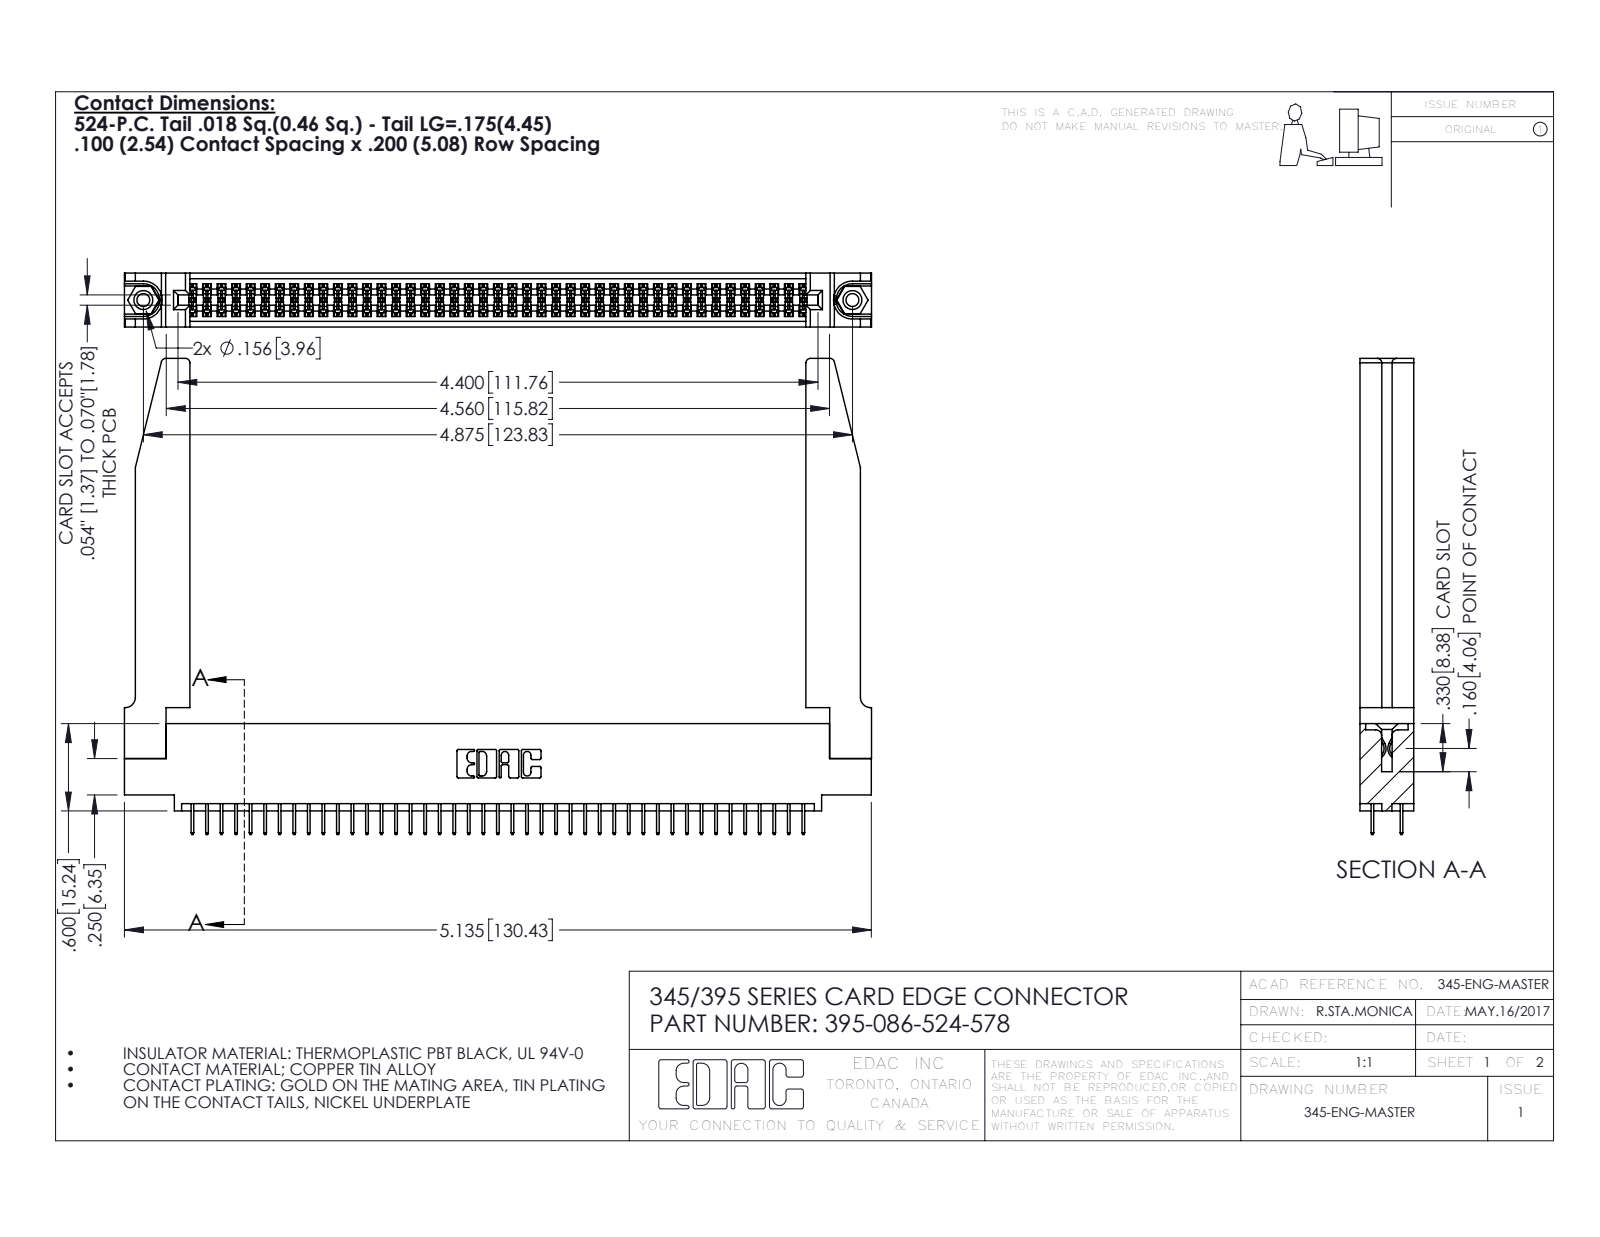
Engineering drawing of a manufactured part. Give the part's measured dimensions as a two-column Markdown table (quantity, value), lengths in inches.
| quantity | value |
| --- | --- |
| part name | 345-292-001_345-293-124; 345-250-001_345-250-001-102; 395-086-524-578; 345-220-078_345-220-078 (+1 more) |
| STEP written by | SolidWorks 2016 (CONFIG_CONTROL_DESIGN) |
| units | inches |
| bodies | 91 solids, 5008 faces (3580 planar, 1376 cylindrical, 52 other) |
| overall size | 5.136 × 3.272 × 0.37 |
| volume | 1.236 in³ |
| surface area | 38.83 in² |
| round holes (diameter × count) | 0.089 × 2, 0.125 × 2, 0.156 × 2, 0.064 × 1 |
| round bosses / shafts (diameter × count) | 0.155 × 2 |
| partial cylindrical surfaces (radius × count) | 0.006 × 129, 0.01 × 22, 0.03 × 8, 0.007 × 6, 0.031 × 6, 0.026 × 3, 0.014 × 2, 0.019 × 2 |
| main face-to-face distances | 0.37, 0.072, 0.298, 0.2, 0.098, 0.272, 0.025, 0.225, 0.148, 0.15 |
| hole center spacings | 0.27, 4.639, 4.875 |
